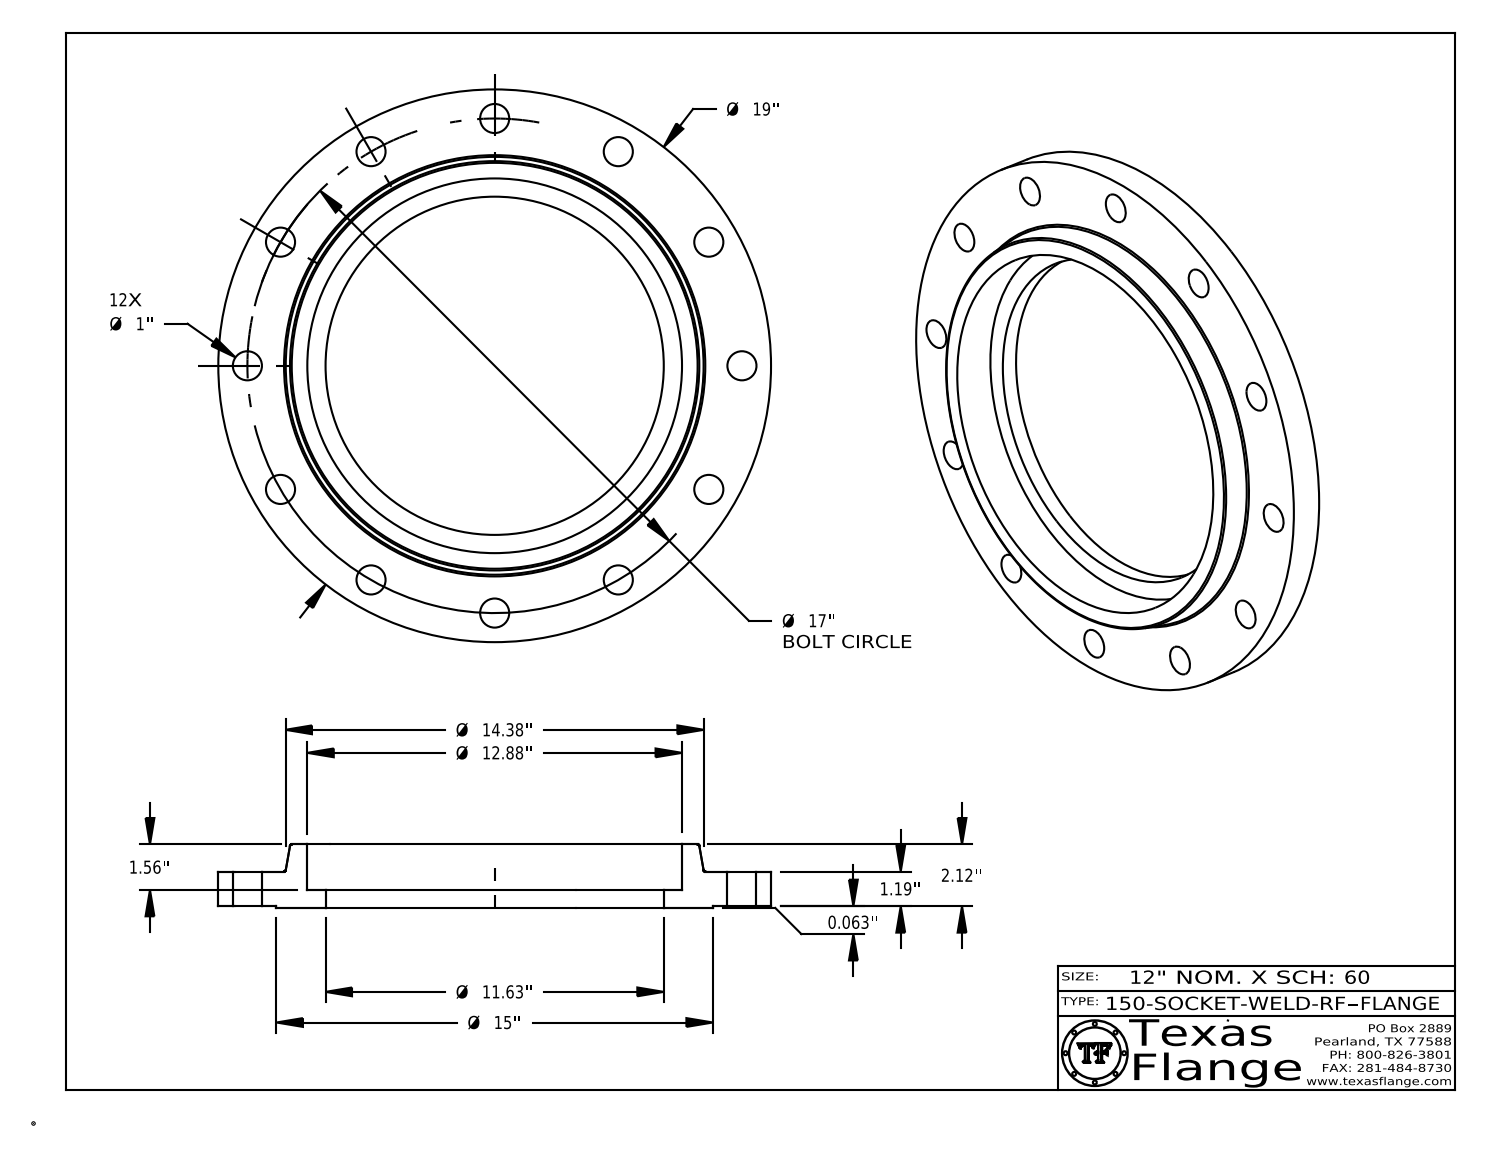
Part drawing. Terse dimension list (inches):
name: 150-SOCKET-WELD-RF
written by: CATIA V5 STEP AP214 (AUTOMOTIVE_DESIGN)
unit: in
bodies: 1 solid, 428 faces (370 planar, 52 cylindrical, 6 other)
size: 19 × 19 × 2.183
volume: 215.5 in³; area: 574 in²
holes: 12× ⌀1, 1× ⌀0.495, 1× ⌀11.626, 1× ⌀12.88
bosses: 8× ⌀0.03, 1× ⌀19, 1× ⌀15, 1× ⌀0.39
face distances: 1.19, 0.063, 1.253, 0.622, 0.56, 0.63, 2.183, 2.12, 1.56, 0.93
hole spacings: 8.5, 16.42, 4.4, 12.02, 14.722, 4.4, 12.021, 14.722
